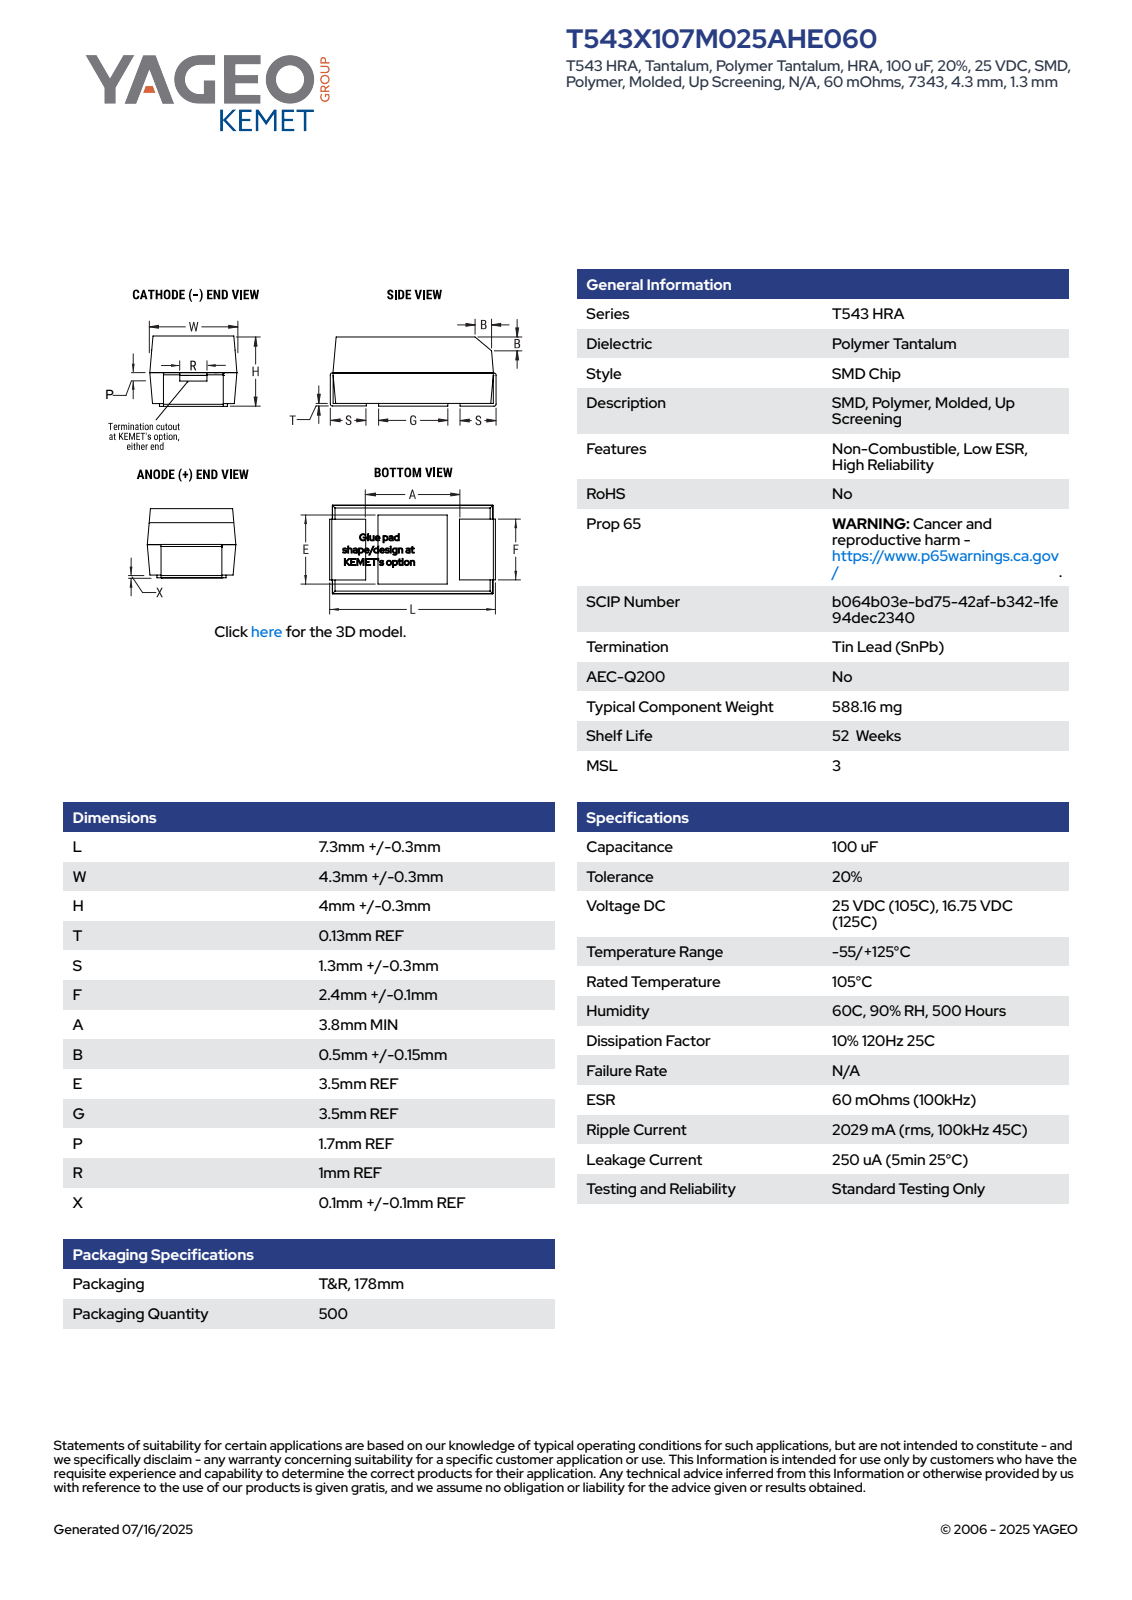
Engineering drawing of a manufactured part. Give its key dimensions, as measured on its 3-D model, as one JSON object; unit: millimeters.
{"part_name": "CTSM_TCM2NK_7343_L7.6W4.6H4.3T0.13S1.3F2.5A3.8B0.65E3.5G3.5P1.7R1X0.2", "step_written_by": "SolidWorks 2020 (AUTOMOTIVE_DESIGN)", "units": "millimeters", "bodies": {"solids": 4, "faces": 100, "planar": 95, "cylindrical": 5, "other": 0}, "overall_size": [7.6, 4.6, 4.3], "volume_mm3": 130, "surface_area_mm2": 186, "partial_cylinders_radius": [[0.1, 4]], "face_to_face_distances": [4.57, 4.3, 4.1, 7.47, 4.17, 7.6, 7.34, 2.05, 5.55, 1.92]}
